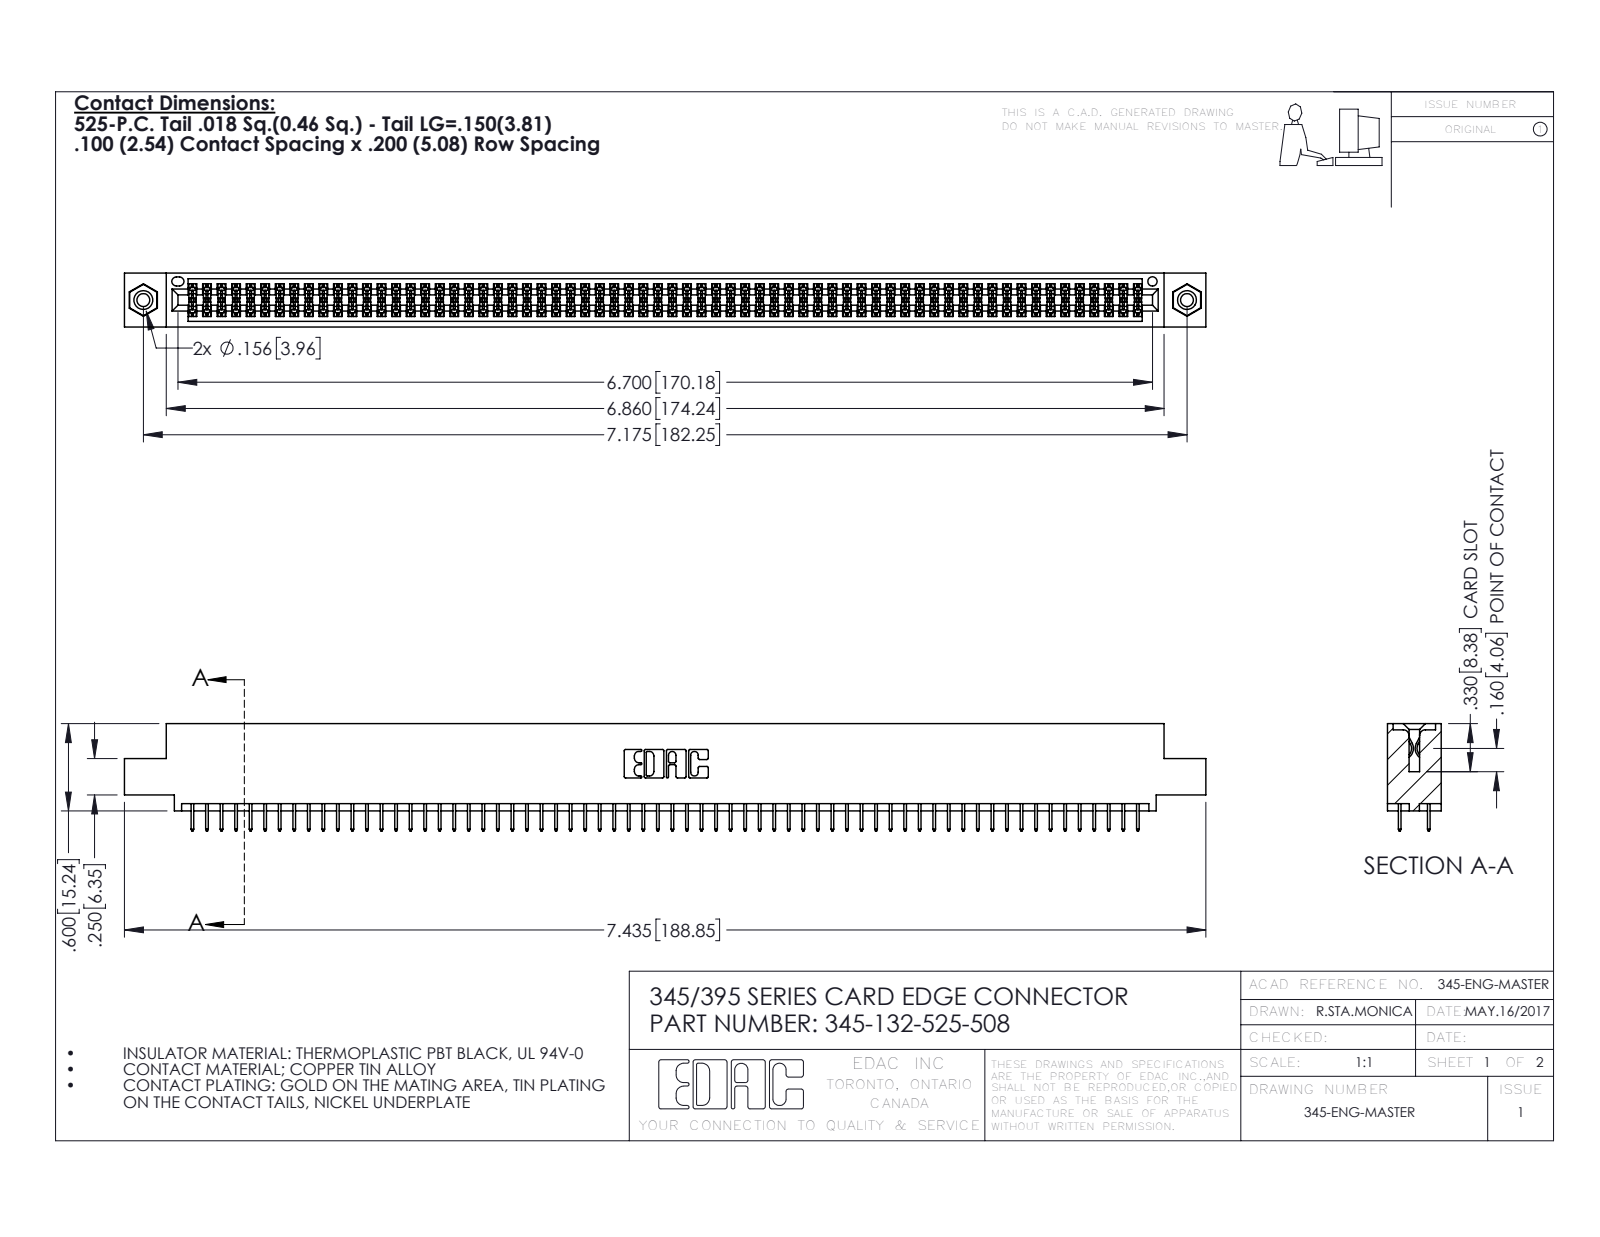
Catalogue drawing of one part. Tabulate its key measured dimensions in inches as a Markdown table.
| quantity | value |
| --- | --- |
| part name | 345-250-001_345-250-003-102; 345-292-001_345-293-125; 345 Part_0.110 Offset - 0.156 Dia-TI; 345-132-525-508 |
| STEP written by | SolidWorks 2020 (CONFIG_CONTROL_DESIGN) |
| units | inches |
| bodies | 135 solids, 7318 faces (5264 planar, 2038 cylindrical, 16 other) |
| overall size | 7.435 × 0.737 × 0.37 |
| volume | 1.115 in³ |
| surface area | 41.73 in² |
| round holes (diameter × count) | 0.089 × 2, 0.125 × 2, 0.156 × 2, 0.064 × 1 |
| round bosses / shafts (diameter × count) | 0.155 × 2 |
| partial cylindrical surfaces (radius × count) | 0.006 × 198, 0.01 × 22, 0.007 × 6, 0.031 × 6, 0.026 × 3, 0.014 × 2, 0.019 × 2, 0.022 × 2 |
| main face-to-face distances | 0.072, 0.298, 0.2, 0.37, 0.098, 0.272, 0.025, 0.225, 0.072, 0.175 |
| hole center spacings | 0.27, 6.939, 7.175 |
